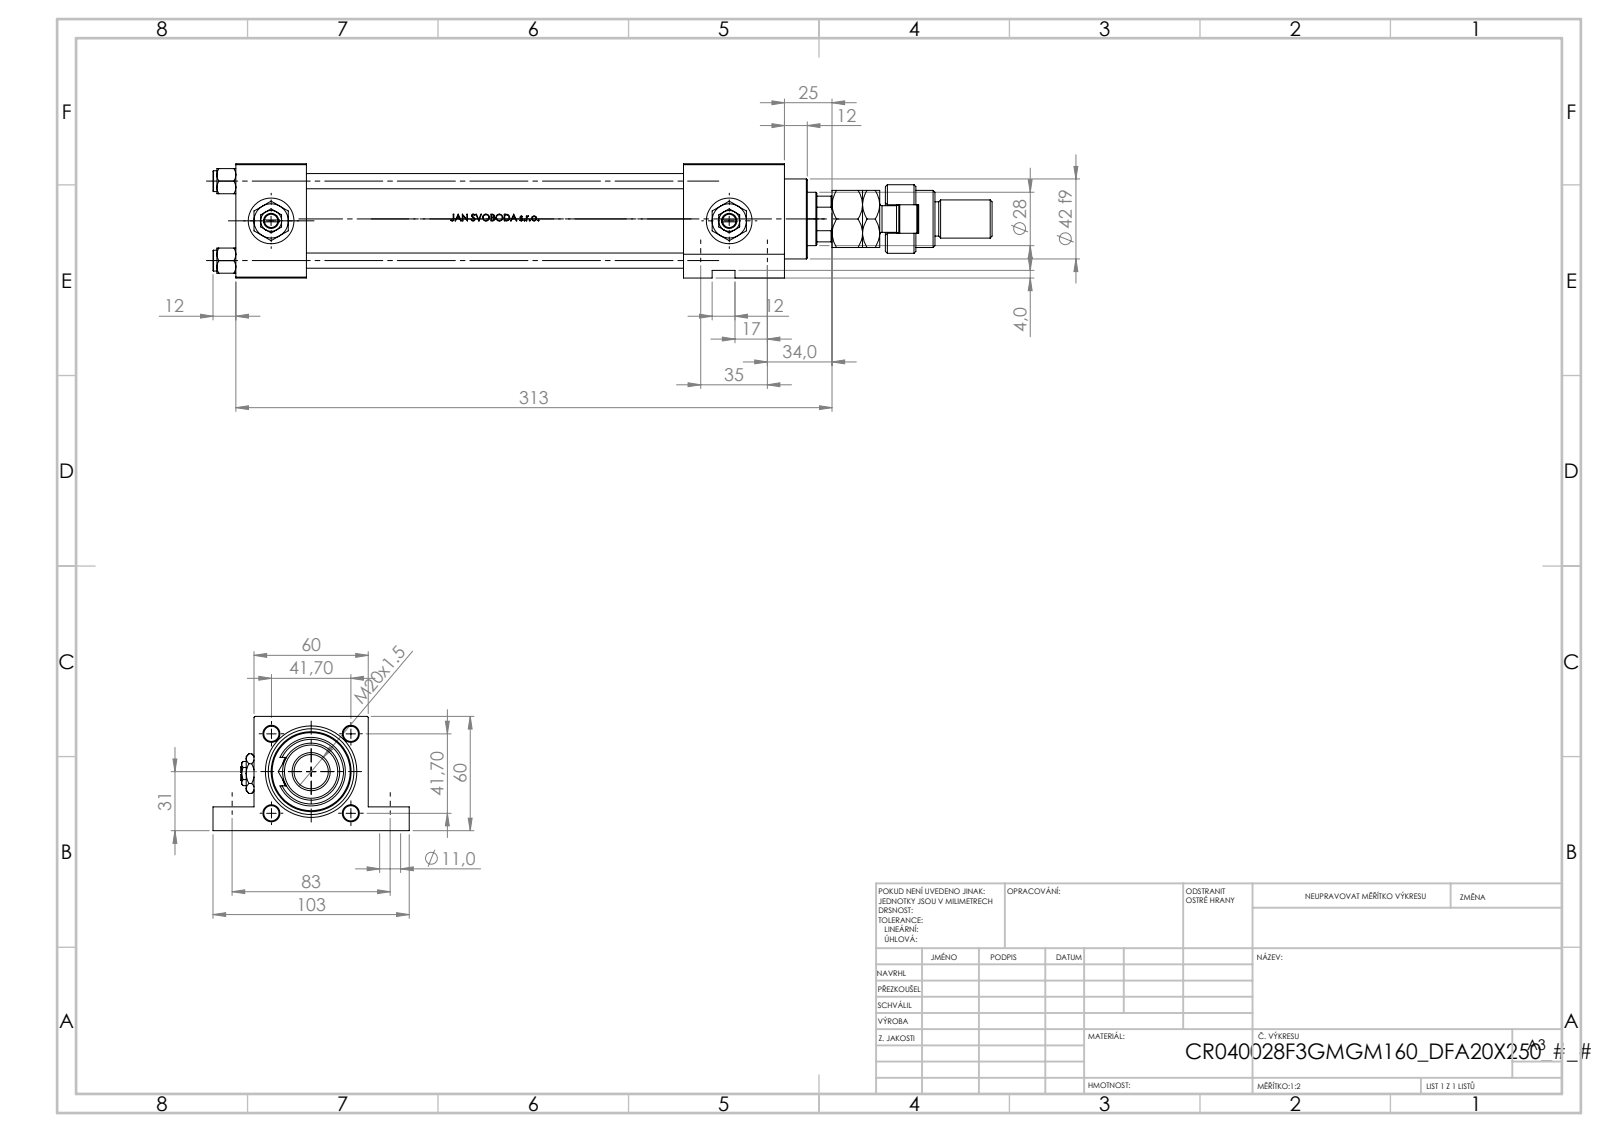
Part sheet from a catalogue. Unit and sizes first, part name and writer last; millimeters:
Units: millimetres
Overall size (bounding box): 409 × 103 × 60
Round holes (diameter × count): ⌀8 ×4, ⌀11 ×4, ⌀16.66 ×3, ⌀24 ×3, ⌀7 ×2, ⌀16 ×1, ⌀18.5 ×1, ⌀28 ×1, ⌀31 ×1, ⌀40 ×1, ⌀45 ×1
Round bosses / shafts (diameter × count): ⌀11 ×4, ⌀46 ×1, ⌀42 ×1, ⌀36 ×1, ⌀30 ×1, ⌀22 ×1, ⌀20 ×1, ⌀18 ×1
Partial cylindrical surfaces — rounded edges, fillets, slot ends (radius × count): R7.5 ×1, R12 ×1, R13.5 ×1
Main face-to-face distances: 60, 37, 53, 235, 198, 288, 38, 251, 12.5, 47.5
Hole centre spacings: 41.7, 28.79, 30.2, 35, 58.97, 83, 90.08, 8
Volume: 661 772 mm³ · Surface area: 198 082 mm²
Bodies: 15 solids, 1300 faces (512 planar, 162 cylindrical, 626 other)
Part name (STEP PRODUCT): V215CR_F_TYCINKA; Zatka_pro_OIL_PORT; FEMALE_PART_FOR_DFA; MFA (+4 more)
STEP written by: SolidWorks 2019 (CONFIG_CONTROL_DESIGN)
